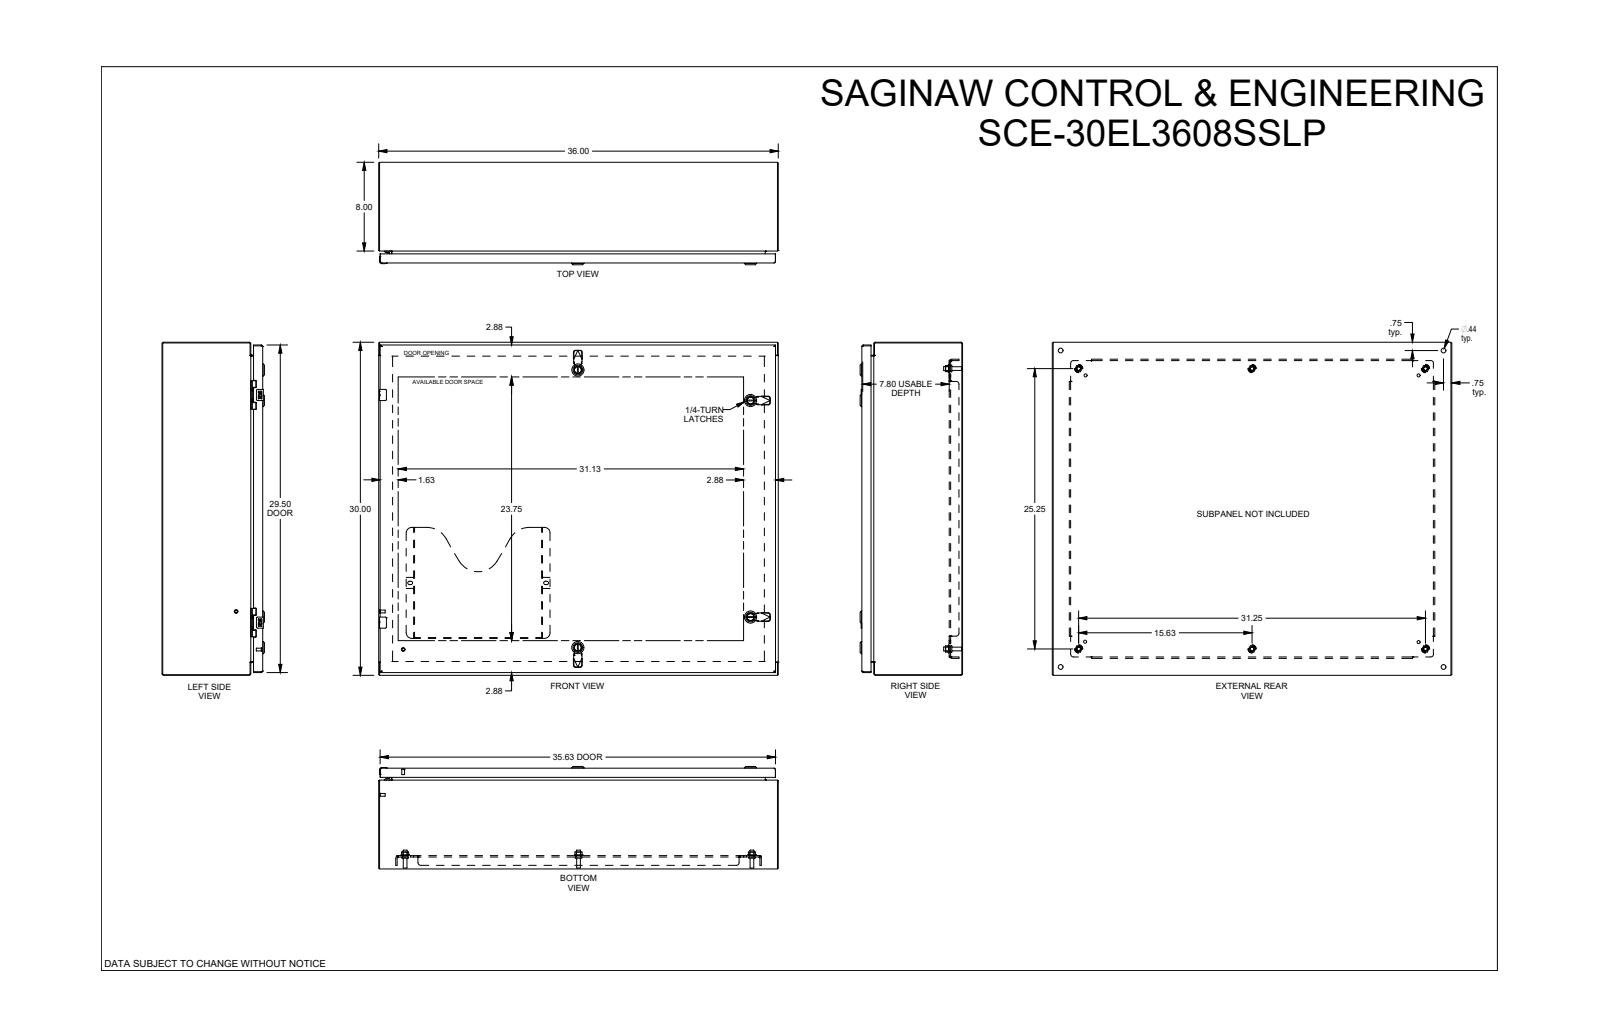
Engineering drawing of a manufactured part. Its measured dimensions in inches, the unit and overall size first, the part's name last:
Units: inches
Overall size (bounding box): 36 × 30 × 9.23
Round holes (diameter × count): ⌀0.367 ×6, ⌀0.5 ×6, ⌀0.172 ×4, ⌀0.197 ×4, ⌀0.205 ×4, ⌀0.244 ×4, ⌀0.266 ×4, ⌀0.281 ×4, ⌀0.315 ×4, ⌀0.394 ×4, ⌀0.437 ×4, ⌀0.634 ×4
Round bosses / shafts (diameter × count): ⌀0.366 ×6, ⌀0.332 ×6, ⌀0.17 ×6, ⌀1.102 ×4, ⌀0.866 ×4, ⌀0.802 ×4, ⌀0.78 ×4, ⌀0.63 ×4
Partial cylindrical surfaces — rounded edges, fillets, slot ends (radius × count): R0.012 ×116, R0.02 ×44, R0.01 ×40, R0.015 ×26, R0.04 ×23, R0.157 ×16, R0.07 ×14, R0.029 ×12
Main face-to-face distances: 0.075, 0.075, 8.923, 8.998, 9.073, 8.998, 1.2, 7.873, 1, 1.125
Hole centre spacings: 20.5, 0.985, 0.02, 4.493, 15.625, 26.924, 29.693, 0.875
Bodies: 0 solids, 3794 faces (1827 planar, 1029 cylindrical, 938 other)
Part name (STEP PRODUCT): SCE-30EL3608SSLP
STEP written by: SolidWorks 2019 (CONFIG_CONTROL_DESIGN)
